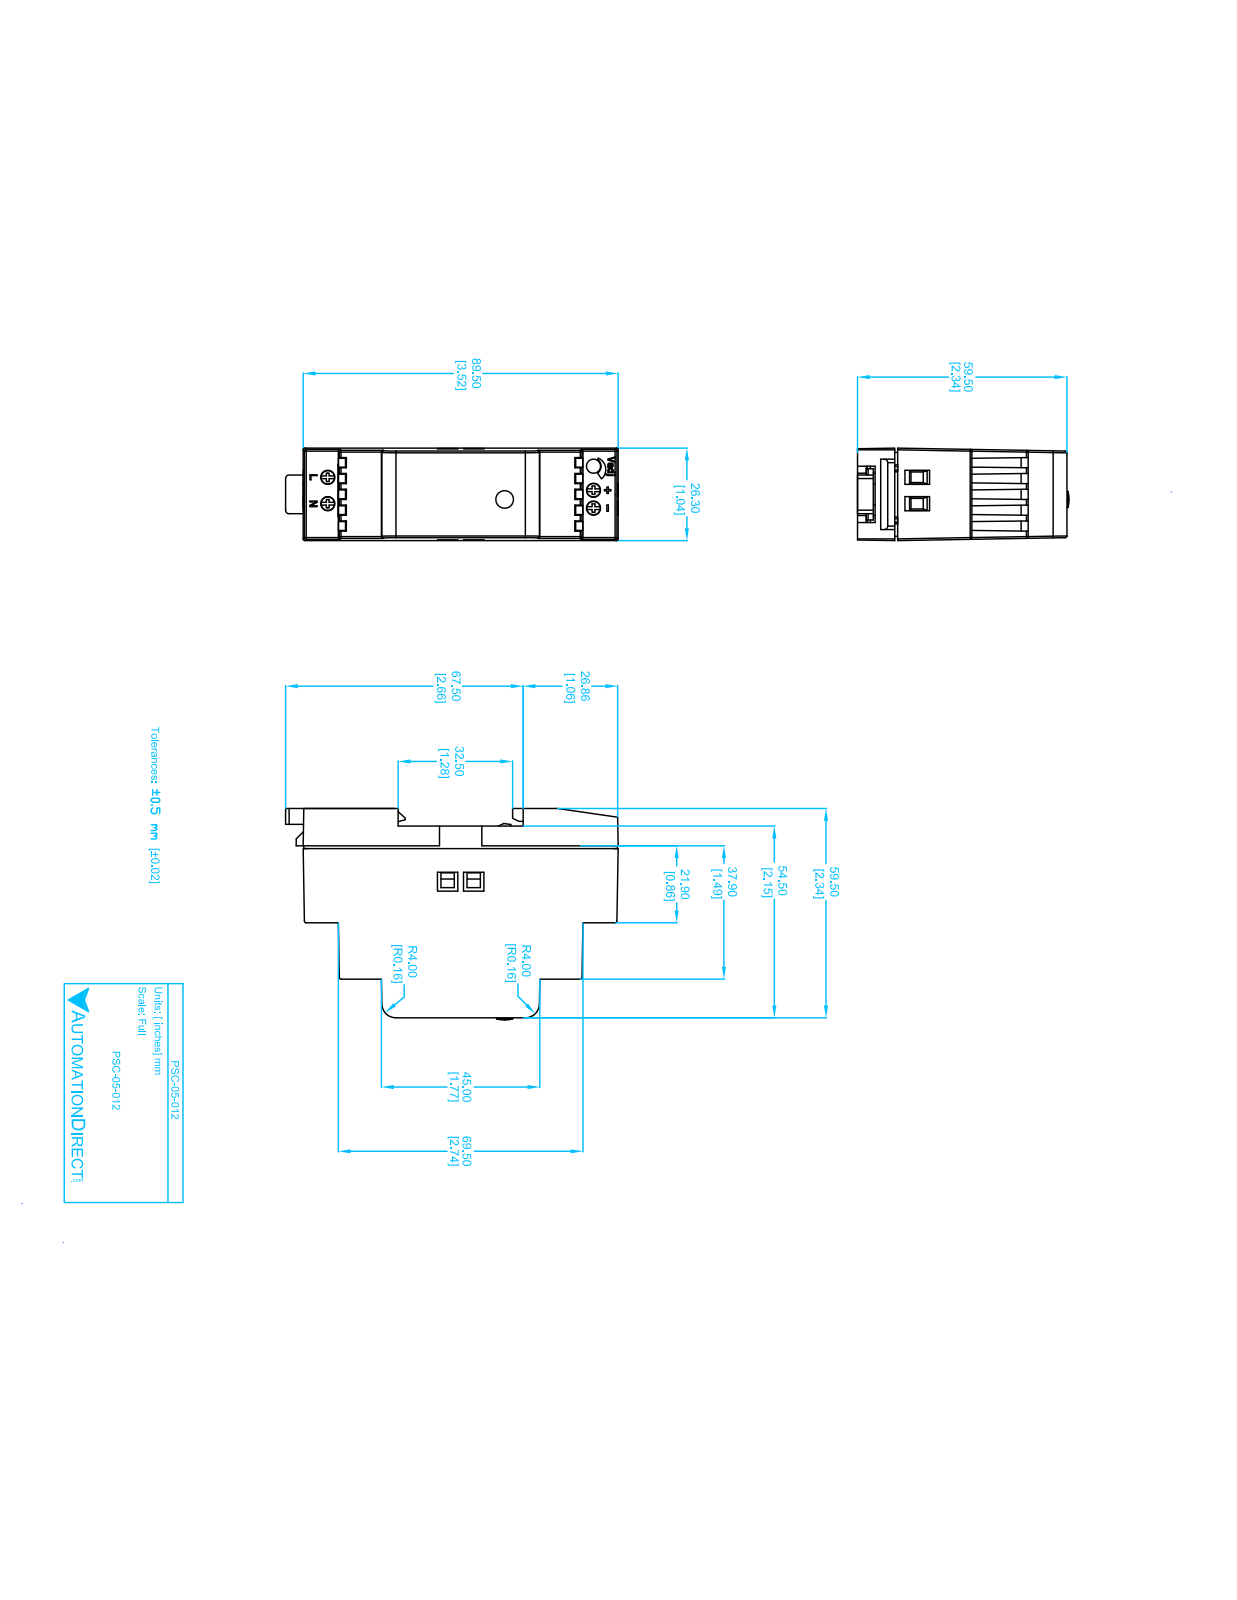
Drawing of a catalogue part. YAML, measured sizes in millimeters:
part_name: "PSC-O5-012"
step_written_by: "SolidWorks 2011 (CONFIG_CONTROL_DESIGN)"
units: millimeters
bodies: {solids: 1, faces: 441, planar: 351, cylindrical: 54, other: 36}
overall_size: [94.5, 60.2, 26.4]
volume: 105700
surface_area: 20710
round_holes:
  - {diameter: 4.1, count: 5}
round_bosses_or_shafts:
  - {diameter: 5.1, count: 1}
partial_cylinders:
  - {radius: 0.5, count: 26}
  - {radius: 1, count: 2}
  - {radius: 4.1, count: 2}
face_to_face_distances: [26.4, 4.8, 15.1, 59.5, 54.6, 48.3, 11.2, 43.4, 11.2, 32.3]
hole_center_spacings: [5.1, 6.4, 7.6, 11.4, 76.7, 76.7, 76.8, 76.9]
